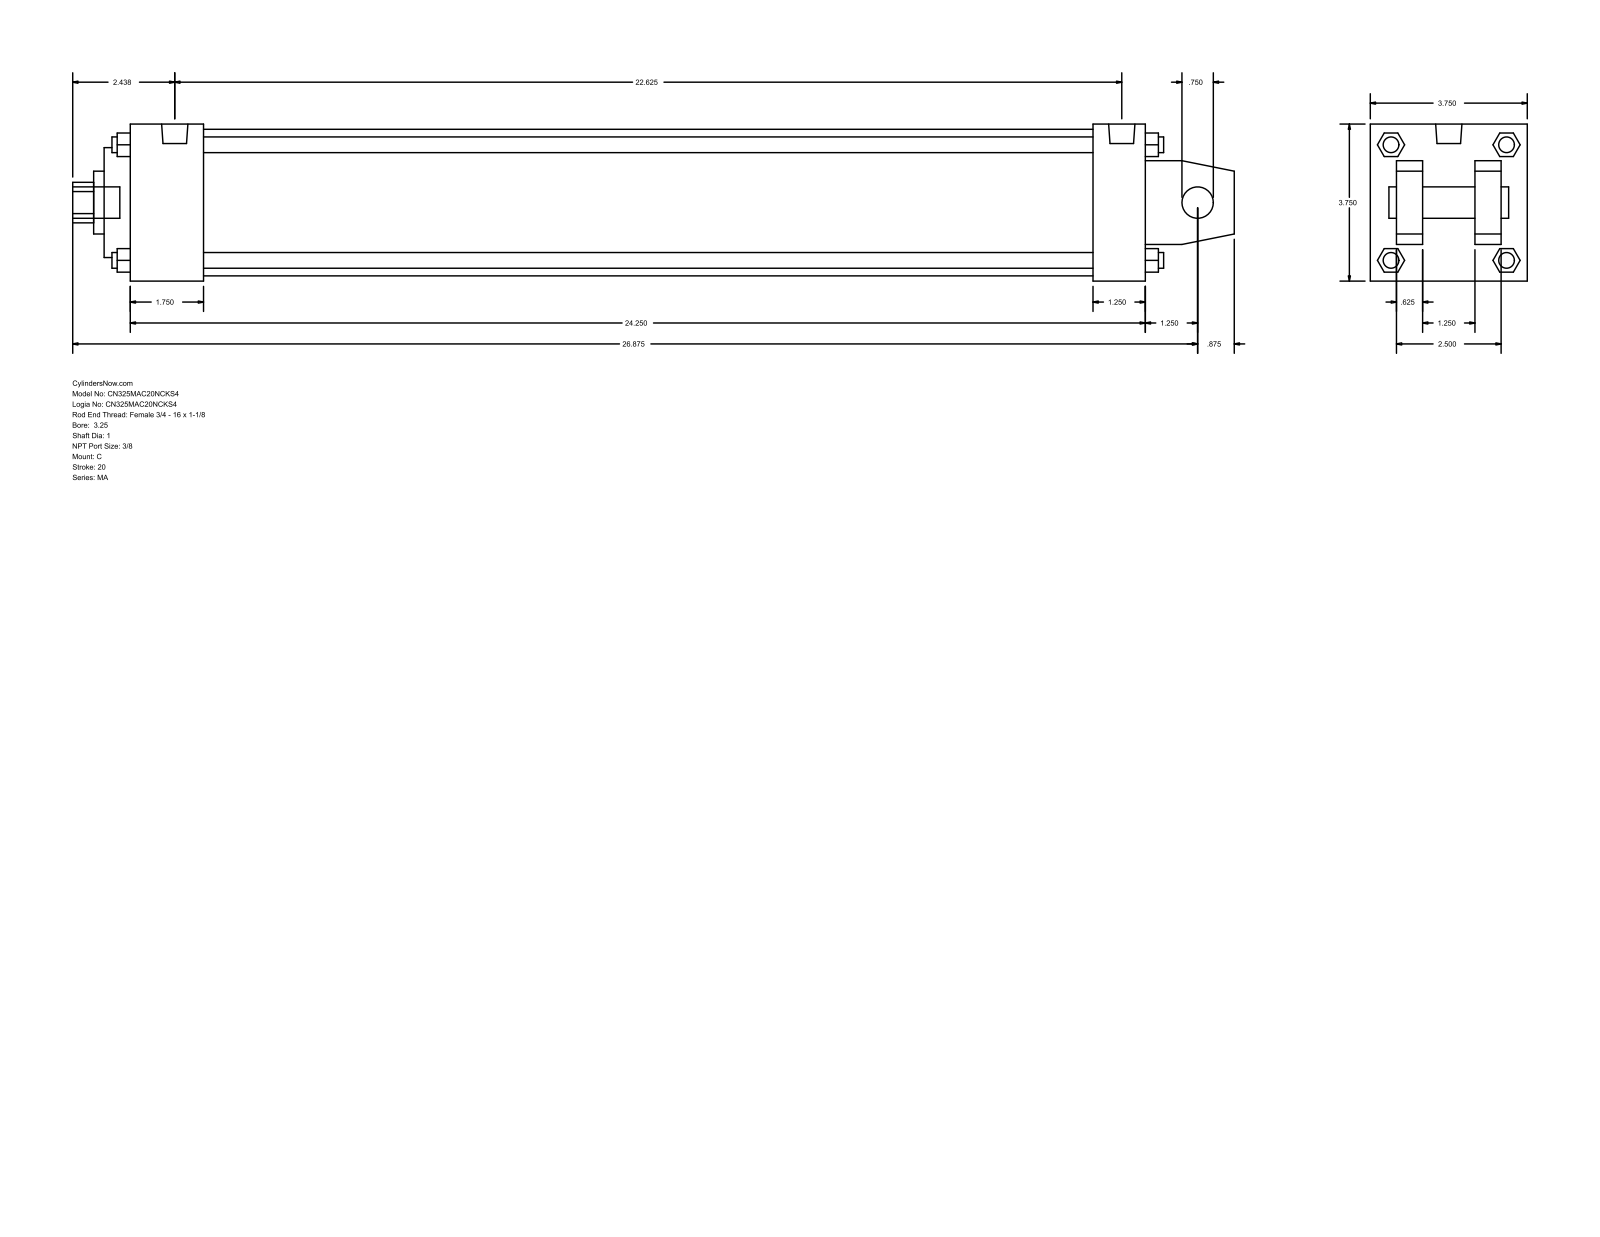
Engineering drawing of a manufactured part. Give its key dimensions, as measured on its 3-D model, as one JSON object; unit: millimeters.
{"part_name": "MA_C__0325_1", "step_written_by": "GSSL Pune (CONFIG_CONTROL_DESIGN)", "units": "millimeters", "bodies": {"solids": 0, "faces": 141, "planar": 109, "cylindrical": 32, "other": 0}, "overall_size": [704.85, 95.25, 95.25], "round_holes": [[19.05, 1], [25.4, 1], [38.1, 1], [66.67, 1], [88.9, 1]], "round_bosses_or_shafts": [[11.11, 4], [9.53, 4], [15.93, 2], [19.05, 1]], "partial_cylinders_radius": [[12.29, 1]], "face_to_face_distances": [95.24, 15.87, 63.5, 615.96, 31.76, 31.74, 79.37, 47.63, 584.2, 44.46]}
